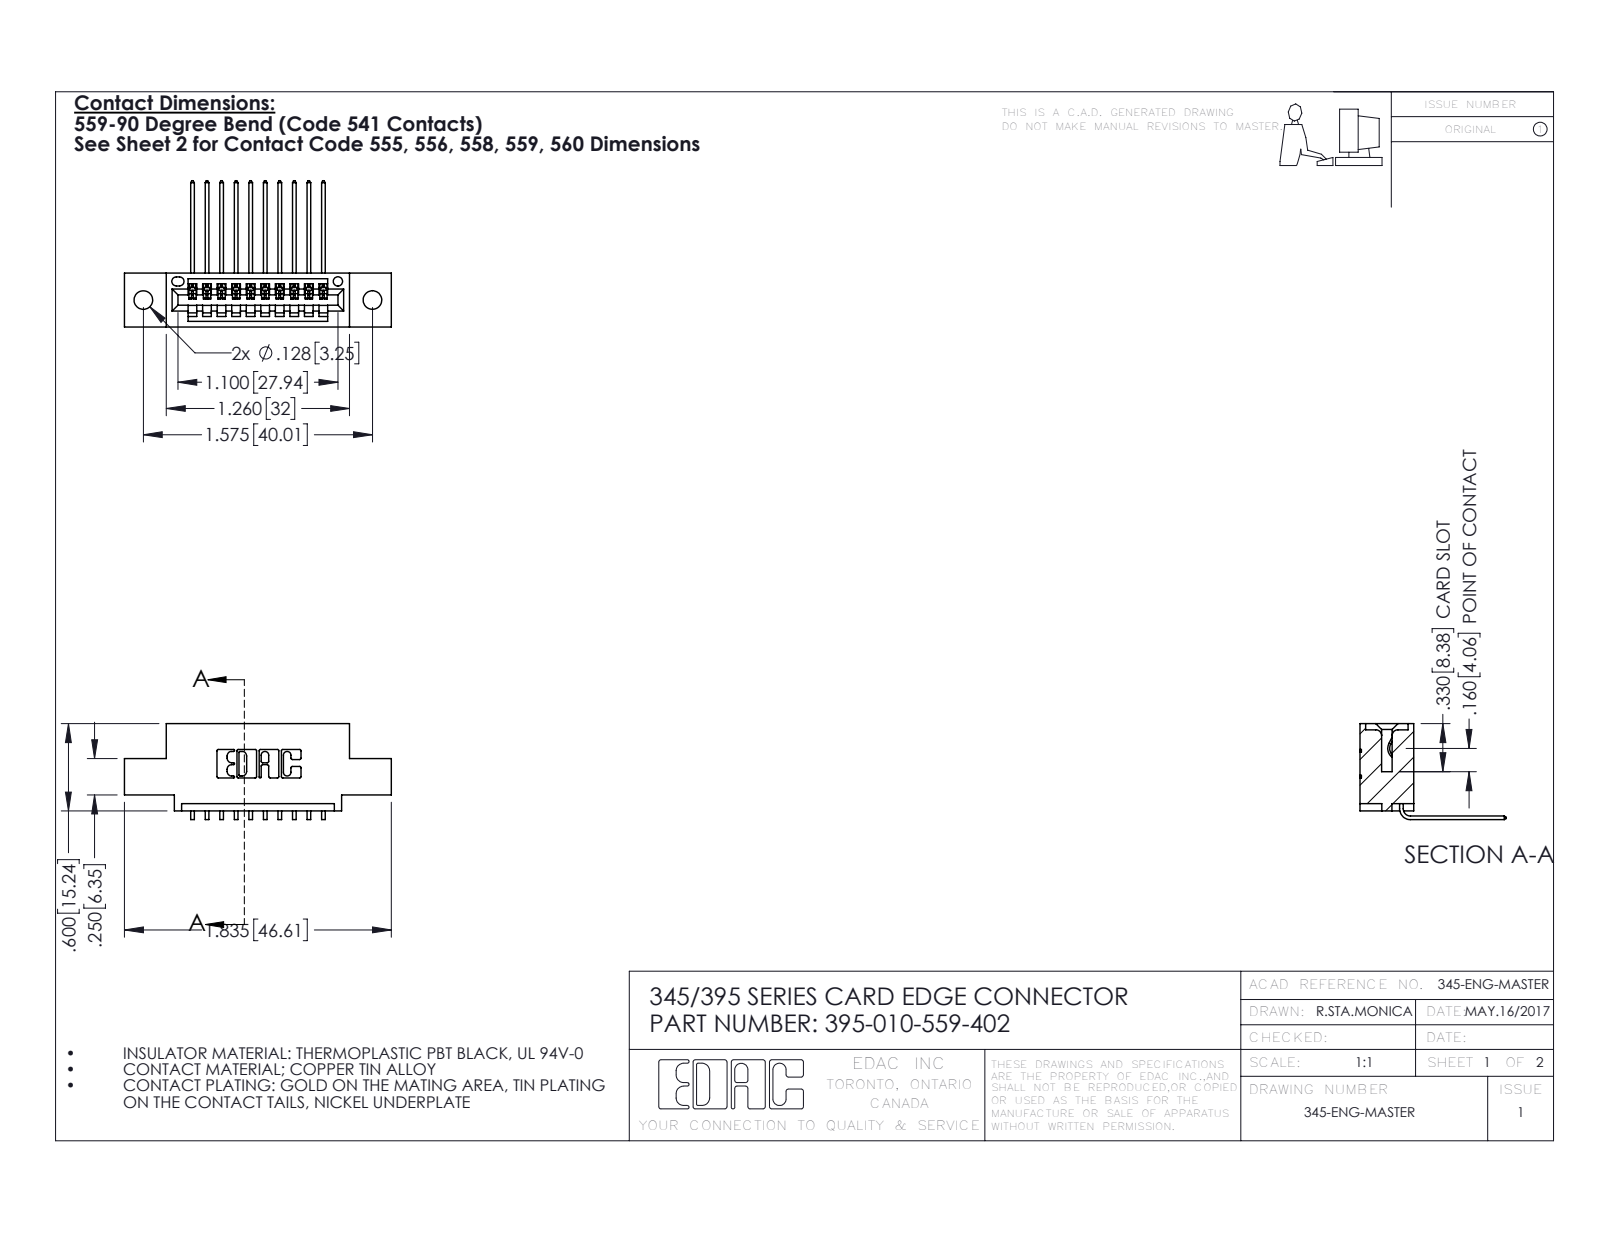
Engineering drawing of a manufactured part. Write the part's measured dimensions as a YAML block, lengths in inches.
part_name: "395-010-559-402; 345 Part_0.110 Offset - 0.128 Dia; 345-292-001_558 559 Tail - 1"
step_written_by: "SolidWorks 2016 (CONFIG_CONTROL_DESIGN)"
units: inches
bodies: {solids: 11, faces: 730, planar: 504, cylindrical: 226, other: 0}
overall_size: [1.835, 1.005, 0.659]
volume: 0.249
surface_area: 7.756
round_holes:
  - {diameter: 0.128, count: 2}
  - {diameter: 0.064, count: 1}
partial_cylinders:
  - {radius: 0.01, count: 22}
  - {radius: 0.006, count: 20}
  - {radius: 0.007, count: 6}
  - {radius: 0.031, count: 6}
  - {radius: 0.026, count: 3}
  - {radius: 0.031, count: 2}
  - {radius: 0.04, count: 2}
  - {radius: 0.014, count: 1}
face_to_face_distances: [0.2, 0.37, 0.072, 0.298, 0.1, 0.6, 0.098, 0.272, 0.025, 0.06]
hole_center_spacings: [0.27, 1.344, 1.575]
